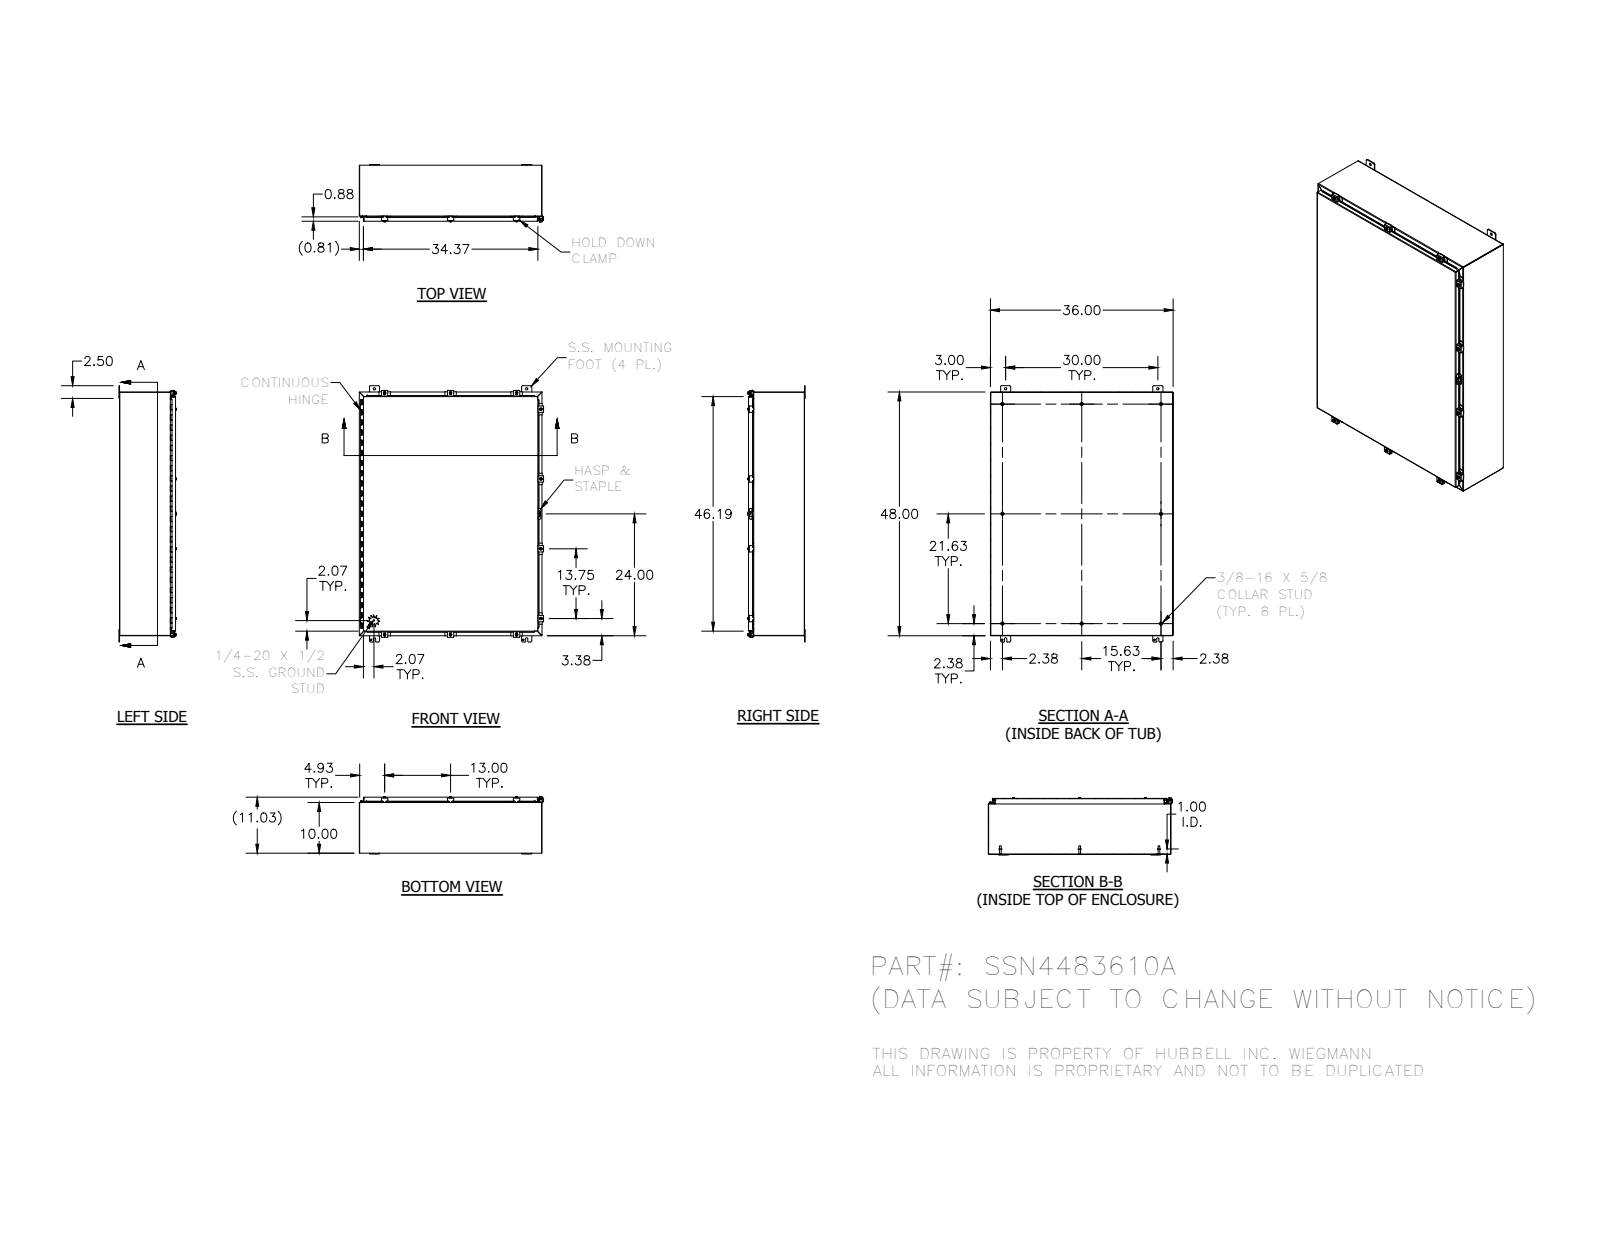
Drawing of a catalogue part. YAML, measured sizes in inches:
part_name: "SSN44836ALID; 30819; HFW30825-4; HFW30825-3 (+8 more)"
step_written_by: "SolidWorks 2014 (AUTOMOTIVE_DESIGN)"
units: inches
bodies: {solids: 73, faces: 2680, planar: 1093, cylindrical: 1174, other: 413}
overall_size: [50.5, 36.311, 11.355]
volume: 438.2
surface_area: 11621
round_holes:
  - {diameter: 0.211, count: 10}
  - {diameter: 0.281, count: 10}
  - {diameter: 0.3, count: 10}
  - {diameter: 0.313, count: 4}
  - {diameter: 0.438, count: 4}
  - {diameter: 0.125, count: 1}
  - {diameter: 0.156, count: 1}
  - {diameter: 0.5, count: 1}
round_bosses_or_shafts:
  - {diameter: 0.25, count: 12}
  - {diameter: 0.52, count: 10}
  - {diameter: 0.5, count: 10}
  - {diameter: 0.35, count: 10}
  - {diameter: 0.625, count: 8}
  - {diameter: 0.33, count: 8}
  - {diameter: 0.337, count: 1}
  - {diameter: 0.12, count: 1}
partial_cylinders:
  - {radius: 0.03, count: 117}
  - {radius: 0.125, count: 41}
  - {radius: 0.25, count: 37}
  - {radius: 0.031, count: 21}
  - {radius: 0.105, count: 21}
  - {radius: 0.141, count: 20}
  - {radius: 0.062, count: 18}
  - {radius: 0.1, count: 14}
face_to_face_distances: [0.074, 10.959, 10.885, 11.033, 35.926, 47.926, 35.852, 36, 9.926, 1.033]
hole_center_spacings: [13.75, 1.593, 13, 18.091, 27.5, 30, 30.973, 48]
